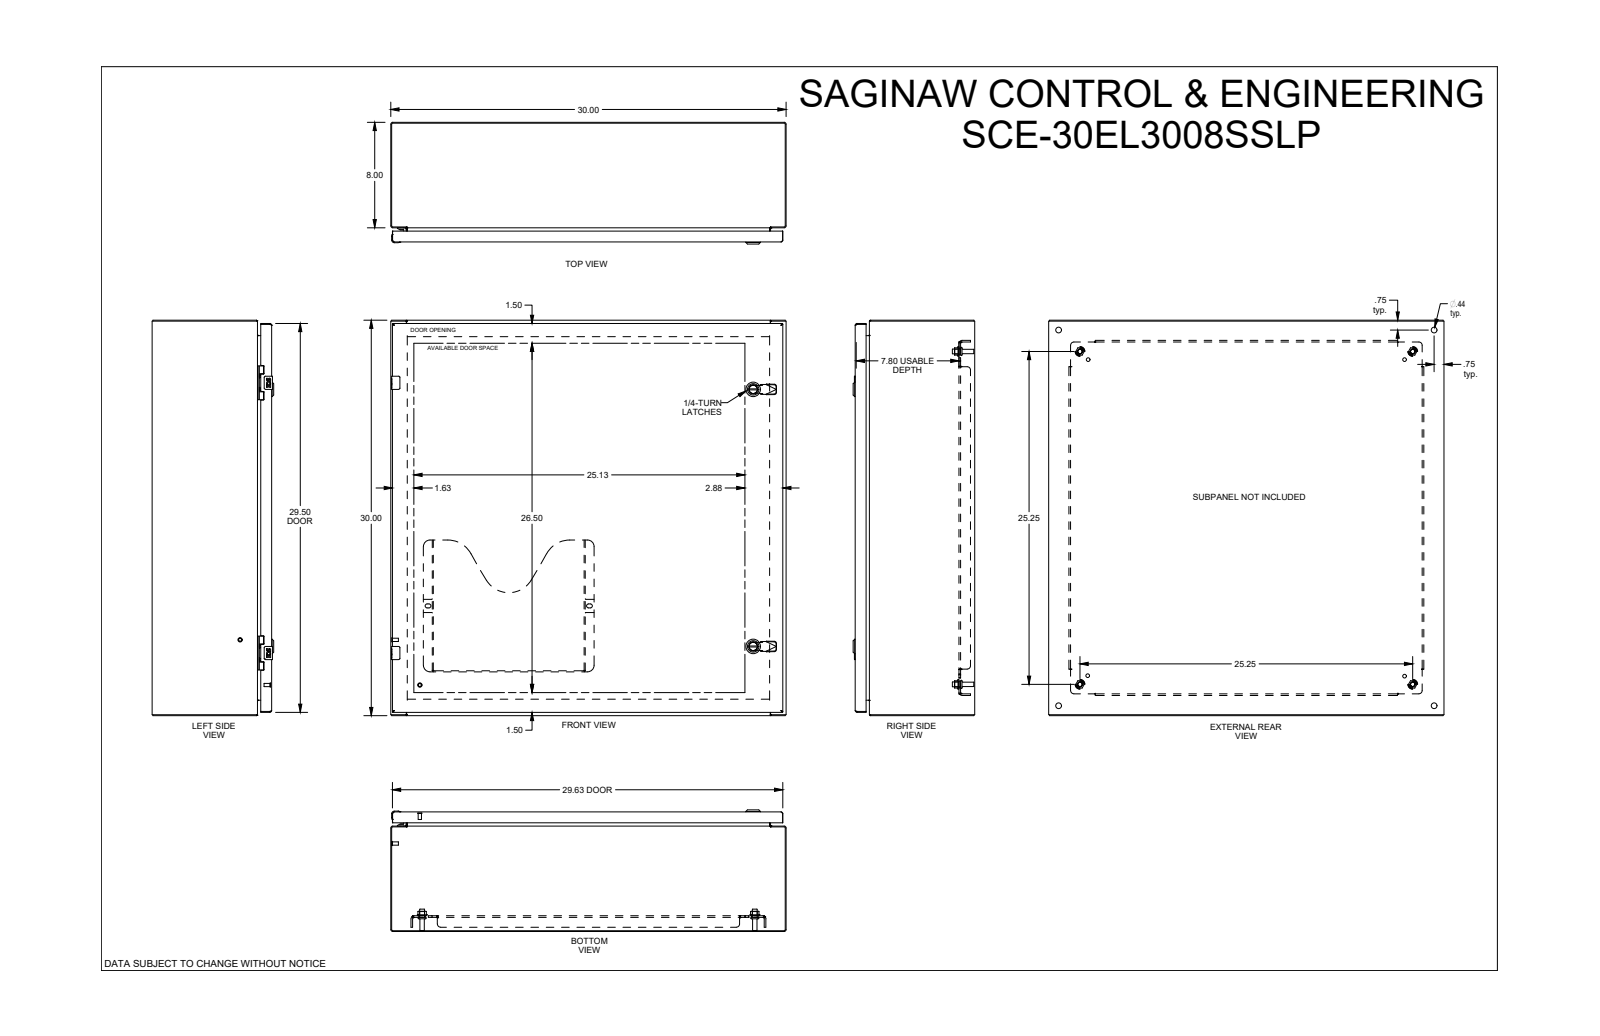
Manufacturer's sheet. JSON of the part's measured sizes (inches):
{"part_name": "SCE-30EL3008SSLP", "step_written_by": "SolidWorks 2019 (CONFIG_CONTROL_DESIGN)", "units": "inches", "bodies": {"solids": 0, "faces": 2838, "planar": 1307, "cylindrical": 759, "other": 772}, "overall_size": [30, 30, 9.23], "round_holes": [[0.172, 4], [0.205, 4], [0.244, 4], [0.266, 4], [0.281, 4], [0.367, 4], [0.437, 4], [0.5, 4], [0.375, 3], [0.156, 2], [0.197, 2], [0.218, 2]], "round_bosses_or_shafts": [[0.17, 6], [0.366, 4], [0.332, 4], [0.25, 4], [0.248, 4], [0.196, 3], [1.102, 2], [0.866, 2]], "partial_cylinders_radius": [[0.012, 56], [0.01, 28], [0.015, 28], [0.04, 23], [0.02, 20], [0.07, 14], [0.029, 12], [0.145, 10]], "face_to_face_distances": [0.075, 29.925, 0.075, 8.923, 8.998, 9.073, 8.998, 1.2, 7.873, 0.125], "hole_center_spacings": [20.5, 0.985, 26.352, 26.924, 24.639, 0.02, 0.875, 4.493]}
